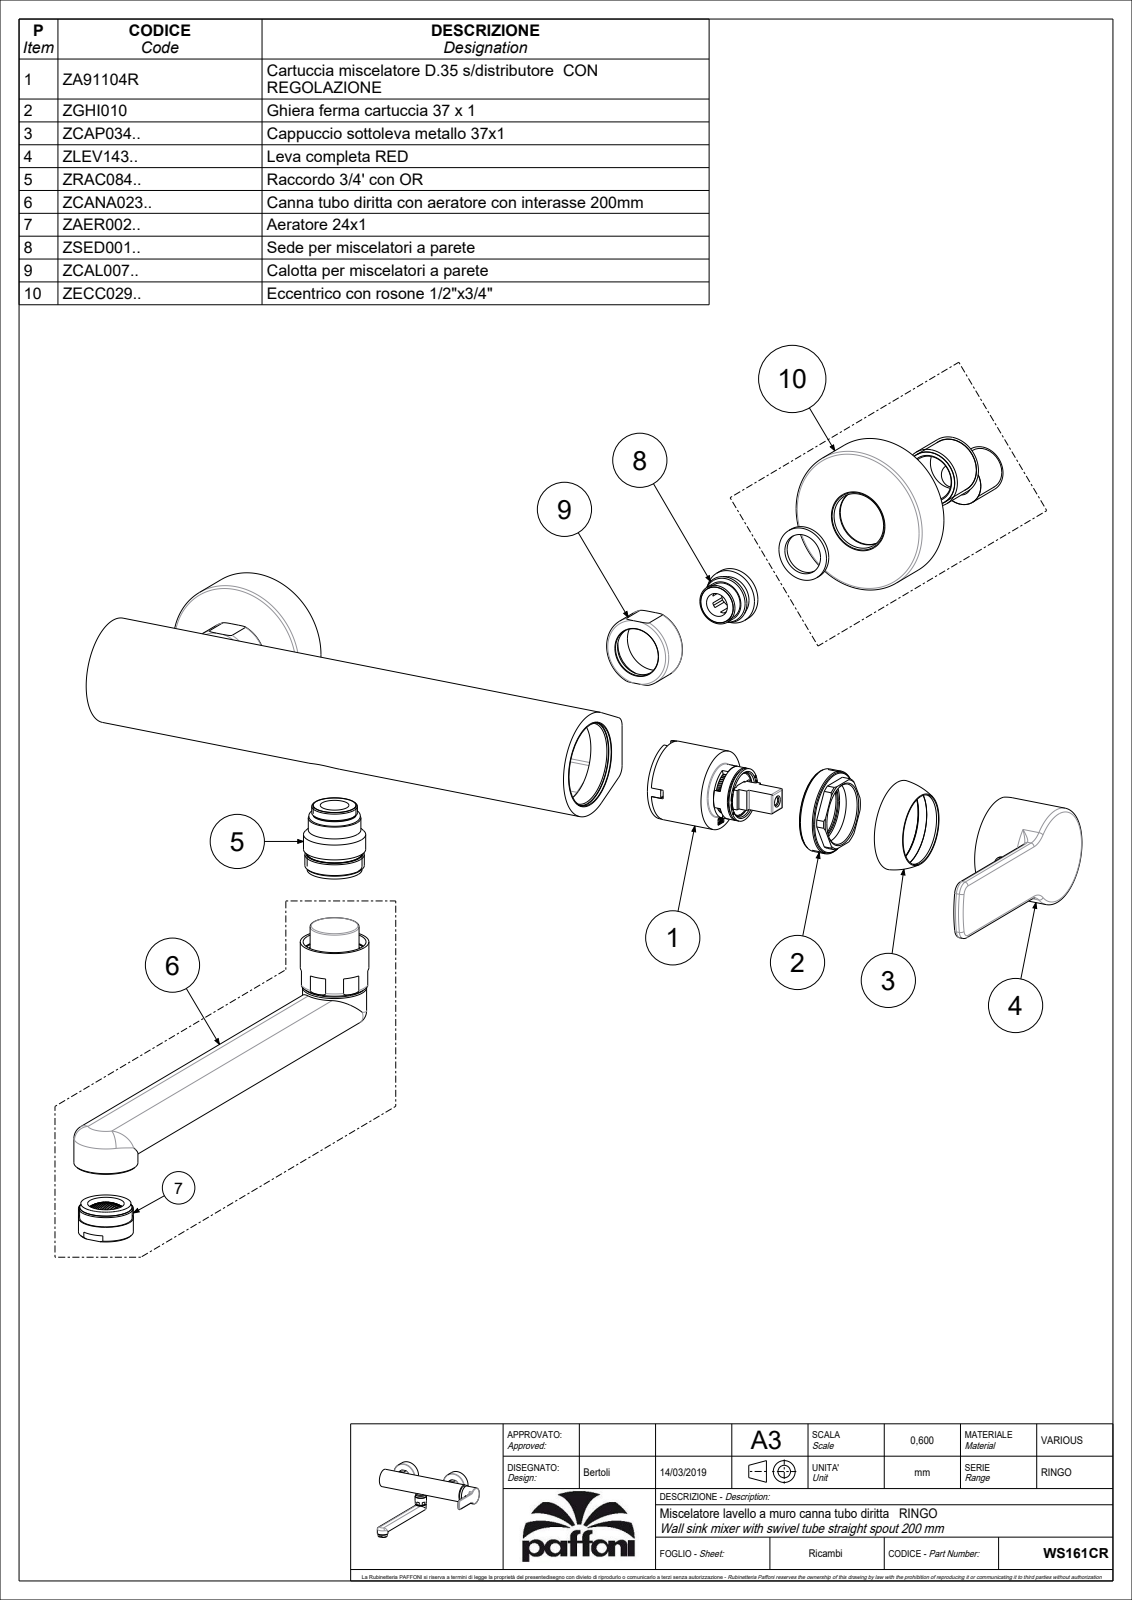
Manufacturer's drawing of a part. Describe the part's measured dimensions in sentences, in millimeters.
The part is named "WS161CR". Its 3-D file was written by "CREO PARAMETRIC BY PTC INC, 2020044 (CONFIG_CONTROL_DESIGN)". It is 3 solids with 3078 faces: 2190 planar, 483 cylindrical and 405 other. Overall it measures 277.83 by 277 by 110.3 millimeters. Its volume is 292 010 cubic millimeters and its surface area 204 910 square millimeters. Round holes: 3 of diameter 7, 3 of diameter 10.5, 3 of diameter 24.5, 2 of diameter 3.3, 2 of diameter 4, 2 of diameter 16, 2 of diameter 18, 2 of diameter 20, 2 of diameter 21.6, 2 of diameter 25, 2 of diameter 26, 2 of diameter 62.3. Round bosses or shafts: 4 of diameter 24, 3 of diameter 28, 2 of diameter 63.5, 2 of diameter 27, 2 of diameter 23, 2 of diameter 19.5, 2 of diameter 17.7, 2 of diameter 16.8. Partial cylindrical surfaces (rounded edges, fillets, slot ends): 66 of radius 0.5, 48 of radius 1.5, 11 of radius 0.15, 4 of radius 0.3, 4 of radius 5, 3 of radius 7, 2 of radius 1, 2 of radius 1.3. The main face-to-face distances are 15, 3.7, 1, 0.6, 29.8, 29.2, 3.5, 14.2, 10.7, 26.3. The hole center spacings are 7.07, 8.6, 11.4, 4, 6, 10, 12.5, 14.
